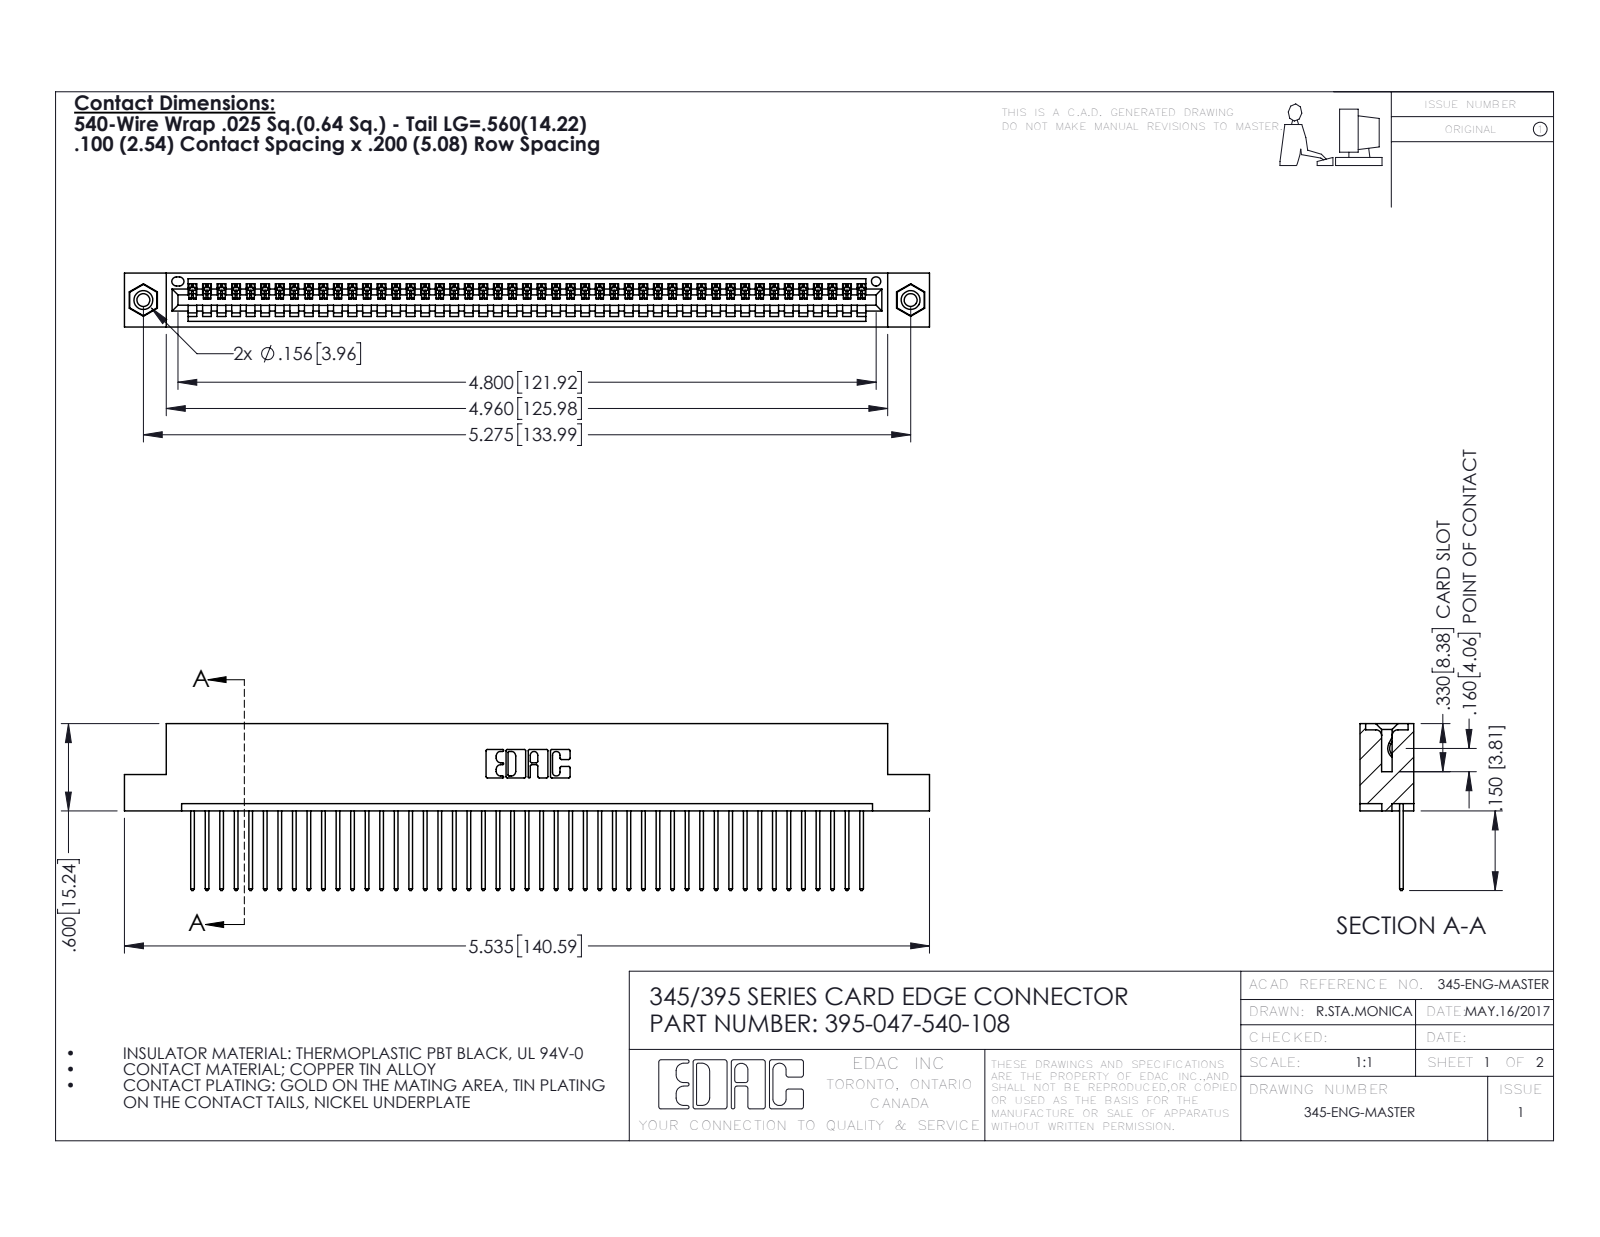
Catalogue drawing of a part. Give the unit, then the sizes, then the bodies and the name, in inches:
Units: inches
Overall size (bounding box): 5.535 × 1.147 × 0.37
Round holes (diameter × count): ⌀0.089 ×2, ⌀0.125 ×2, ⌀0.156 ×2, ⌀0.064 ×1
Round bosses / shafts (diameter × count): ⌀0.155 ×2
Partial cylindrical surfaces — rounded edges, fillets, slot ends (radius × count): R0.006 ×94, R0.01 ×94, R0.01 ×22, R0.007 ×6, R0.031 ×6, R0.026 ×3, R0.031 ×2, R0.04 ×2
Main face-to-face distances: 0.072, 0.298, 0.37, 0.2, 0.098, 0.272, 0.025, 0.225, 0.149, 0.072
Hole centre spacings: 0.27, 5.039, 5.275
Volume: 0.821 in³ · Surface area: 28.55 in²
Bodies: 50 solids, 2912 faces (1992 planar, 904 cylindrical, 16 other)
Part name (STEP PRODUCT): 345 Part_Flush Mounting Lugs - 0.156 Dia-TI; 345-250-001_345-250-003-102; 395-047-540-108; 345-292-001_345-293-140
STEP written by: SolidWorks 2016 (CONFIG_CONTROL_DESIGN)
